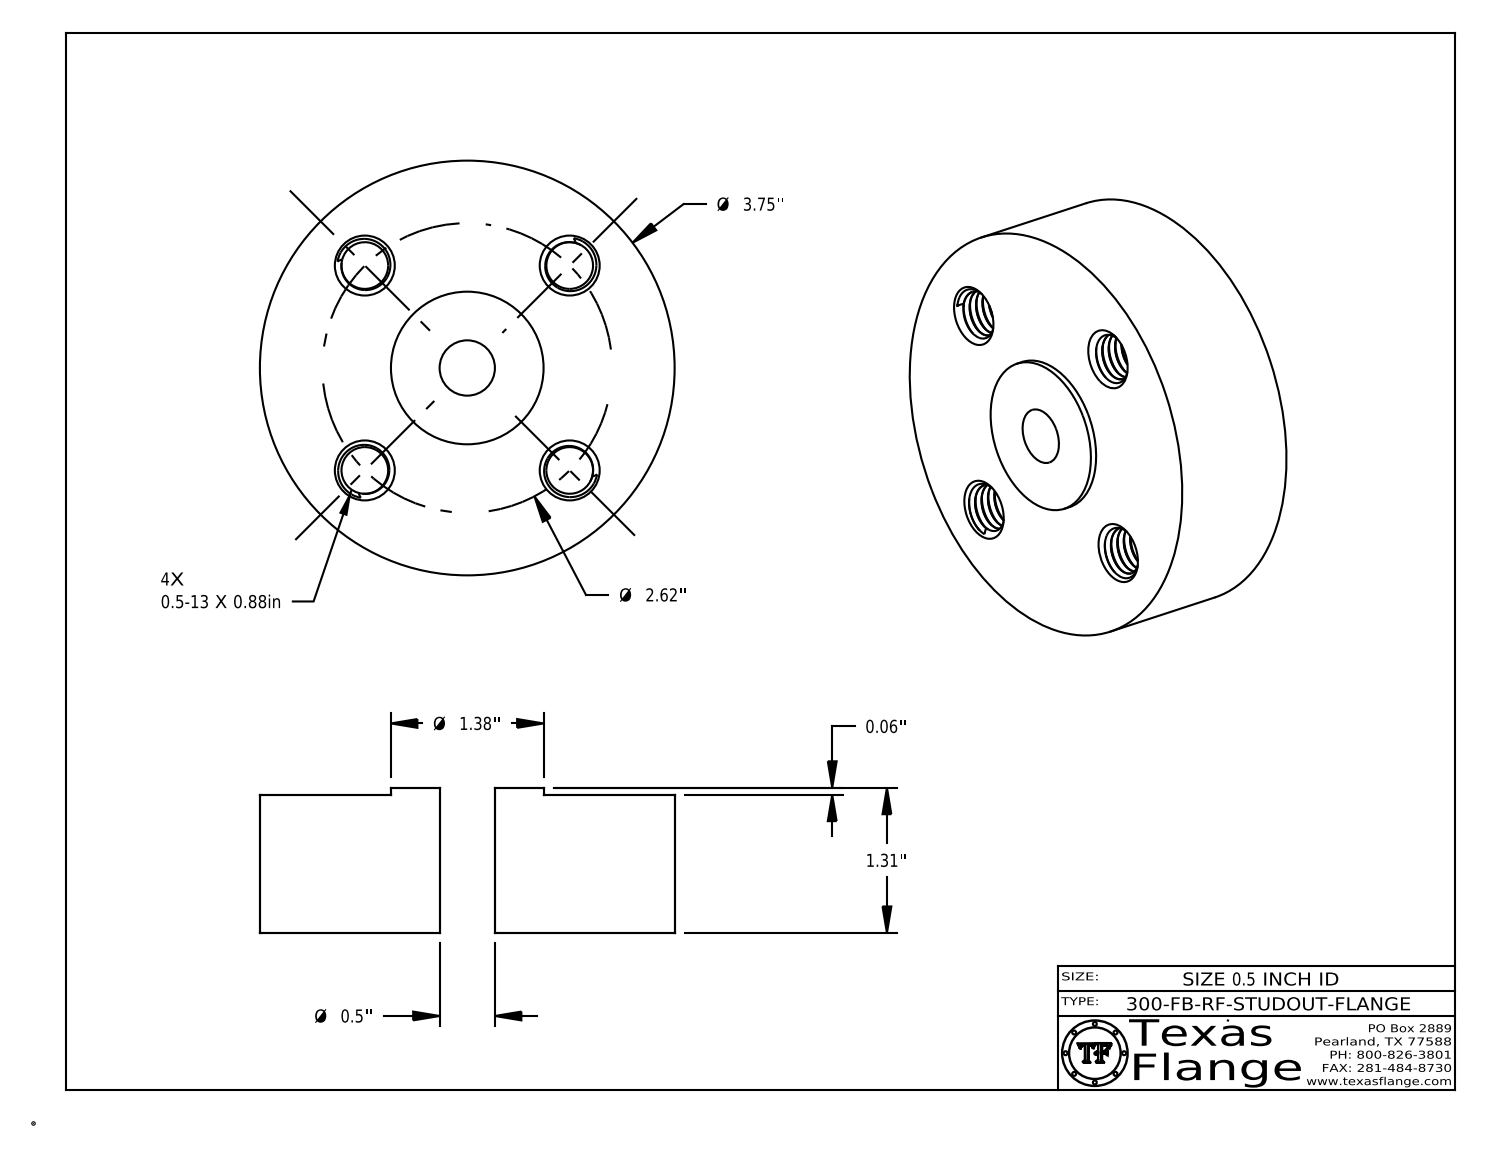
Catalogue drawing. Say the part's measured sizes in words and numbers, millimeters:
The part is named "0.5-300-FB-RF-STUDOUT-FLANGE". Its 3-D file was written by "CATIA V5 STEP AP214 (AUTOMOTIVE_DESIGN)". It is 1 solid with 586 faces: 368 planar, 82 cylindrical and 136 other. Overall it measures 95.3 by 95.3 by 33.4 millimeters. Its volume is 214 000 cubic millimeters and its surface area 28 990 square millimeters. Round holes: 4 of diameter 10.7, 1 of diameter 12.7, 1 of diameter 25.4. Round bosses or shafts: 8 of diameter 1.5, 1 of diameter 95.3, 1 of diameter 35.1, 1 of diameter 20. The main face-to-face distances are 31.8, 1.6, 33.4, 0.4, 33, 31.4, 7.6, 7.4, 1.4, 6.3. The hole center spacings are 33.3, 47.1, 25.5, 61.5, 66.5, 33.3.
